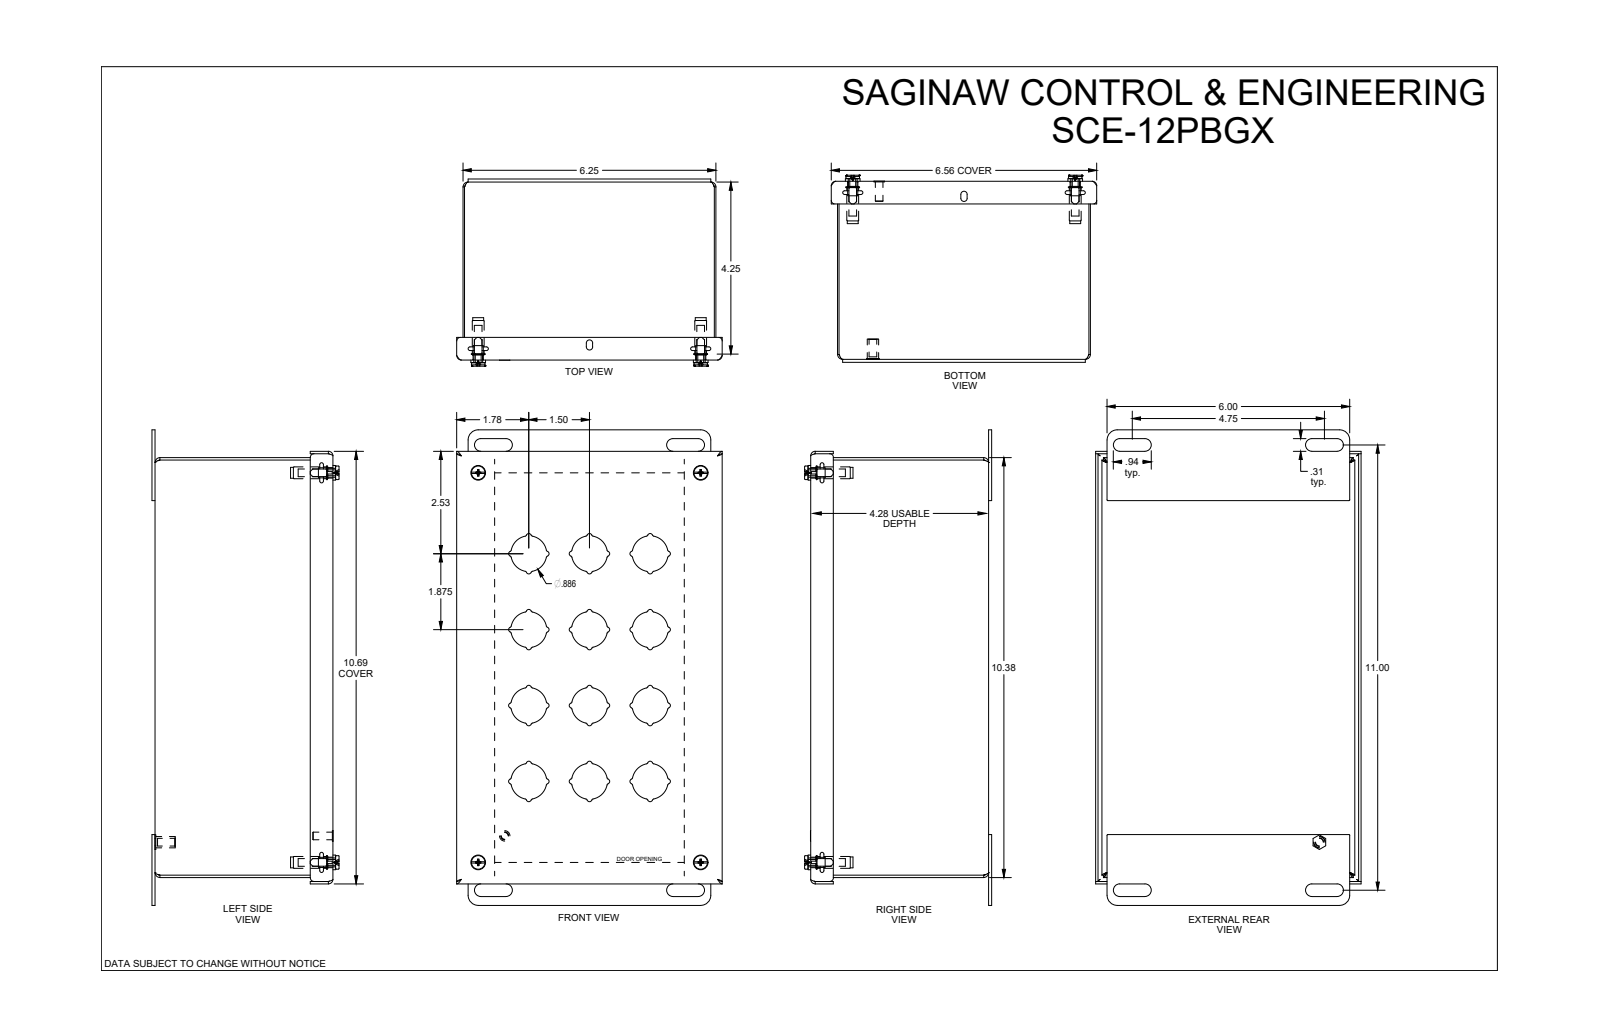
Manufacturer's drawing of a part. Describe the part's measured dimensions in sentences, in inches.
The part is named "SCE-12PBGX". Its 3-D file was written by "SolidWorks 2019 (AUTOMOTIVE_DESIGN)". It is 15 solids with 612 faces: 166 planar, 370 cylindrical and 76 other. Overall it measures 11.75 by 6.563 by 4.536 inches. Its volume is 20.34 cubic inches and its surface area 675.3 square inches. Round holes: 5 of diameter 0.19, 4 of diameter 0.22, 4 of diameter 0.25, 4 of diameter 0.266, 4 of diameter 0.317, 1 of diameter 0.193, 1 of diameter 0.28. Round bosses or shafts: 4 of diameter 0.437, 4 of diameter 0.362, 4 of diameter 0.34, 4 of diameter 0.292, 4 of diameter 0.27, 4 of diameter 0.26, 1 of diameter 0.28, 1 of diameter 0.256. Partial cylindrical surfaces (rounded edges, fillets, slot ends): 96 of radius 0.04, 48 of radius 0.062, 20 of radius 0.06, 12 of radius 0.443, 8 of radius 0.015, 8 of radius 0.115, 8 of radius 0.156, 8 of radius 0.245. The main face-to-face distances are 0.06, 4.338, 6.19, 4.278, 4.398, 10.315, 6.25, 6.13, 4.19, 0.148. The hole center spacings are 9.625, 5.507, 11.085, 9.624, 9.625, 11.089, 5.025, 5.5.
